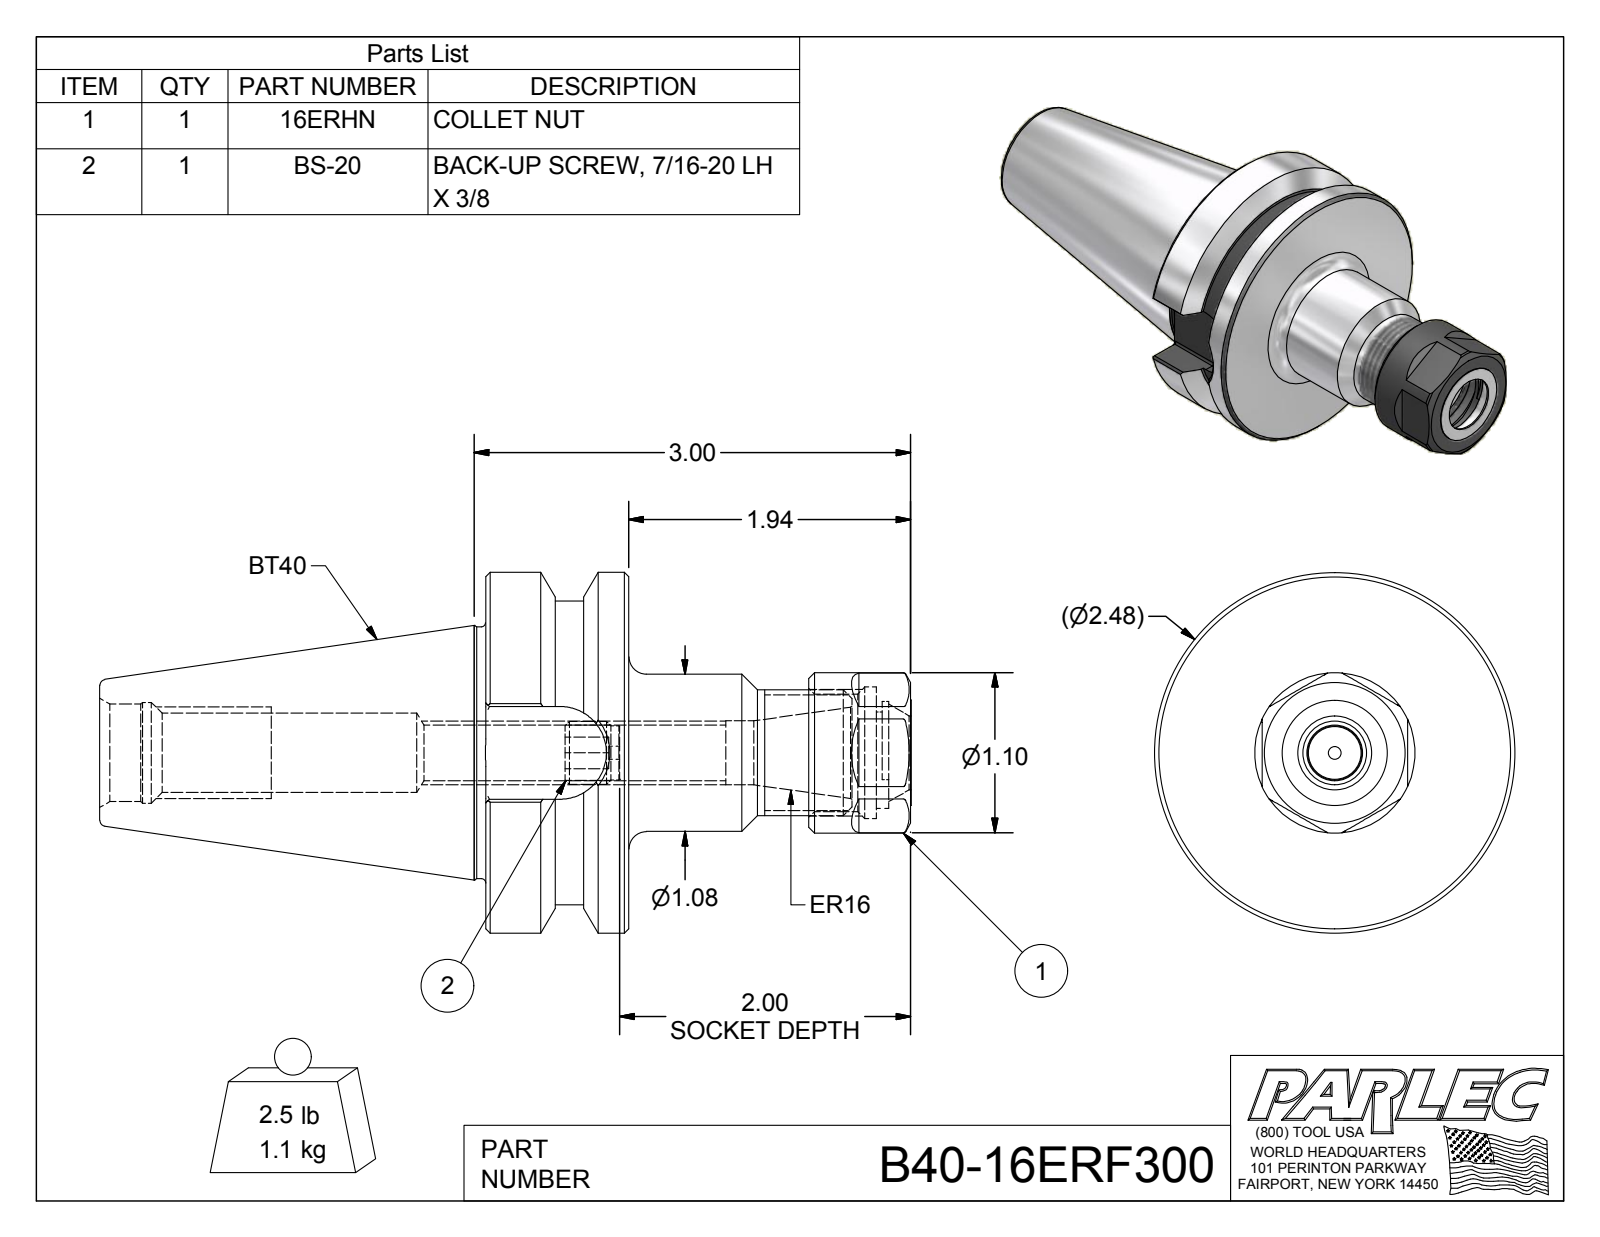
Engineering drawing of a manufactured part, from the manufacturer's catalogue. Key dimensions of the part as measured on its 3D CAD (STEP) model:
Part name (STEP PRODUCT): B40-16ER3-1; 16ERHN; BS-20; B40-16ERF300
STEP written by: Autodesk Inventor 2016 (AUTOMOTIVE_DESIGN)
Units: millimetres
Bodies: 3 solids, 121 faces (50 planar, 33 cylindrical, 38 other)
Overall size (bounding box): 141.6 × 62.99 × 62.99
Volume: 142 622 mm³ · Surface area: 30 195 mm²
Round holes (diameter × count): ⌀2.29 ×1, ⌀9.73 ×1, ⌀11.18 ×1, ⌀12.4 ×1, ⌀13.84 ×1, ⌀17.01 ×1, ⌀17.02 ×1, ⌀17.62 ×1, ⌀20.5 ×1, ⌀23 ×1
Round bosses / shafts (diameter × count): ⌀62.99 ×1, ⌀53.01 ×1, ⌀43.94 ×1, ⌀28 ×1, ⌀27.43 ×1, ⌀22 ×1, ⌀10.97 ×1, ⌀9.46 ×1
Partial cylindrical surfaces — rounded edges, fillets, slot ends (radius × count): R0.51 ×8, R7.24 ×1, R8.09 ×1, R9 ×1
Main face-to-face distances: 24.99, 74.22, 49.23, 25.14, 45.22, 10.04, 35.18, 68.52, 43.53, 5.7
Hole centre spacings: 1.52
